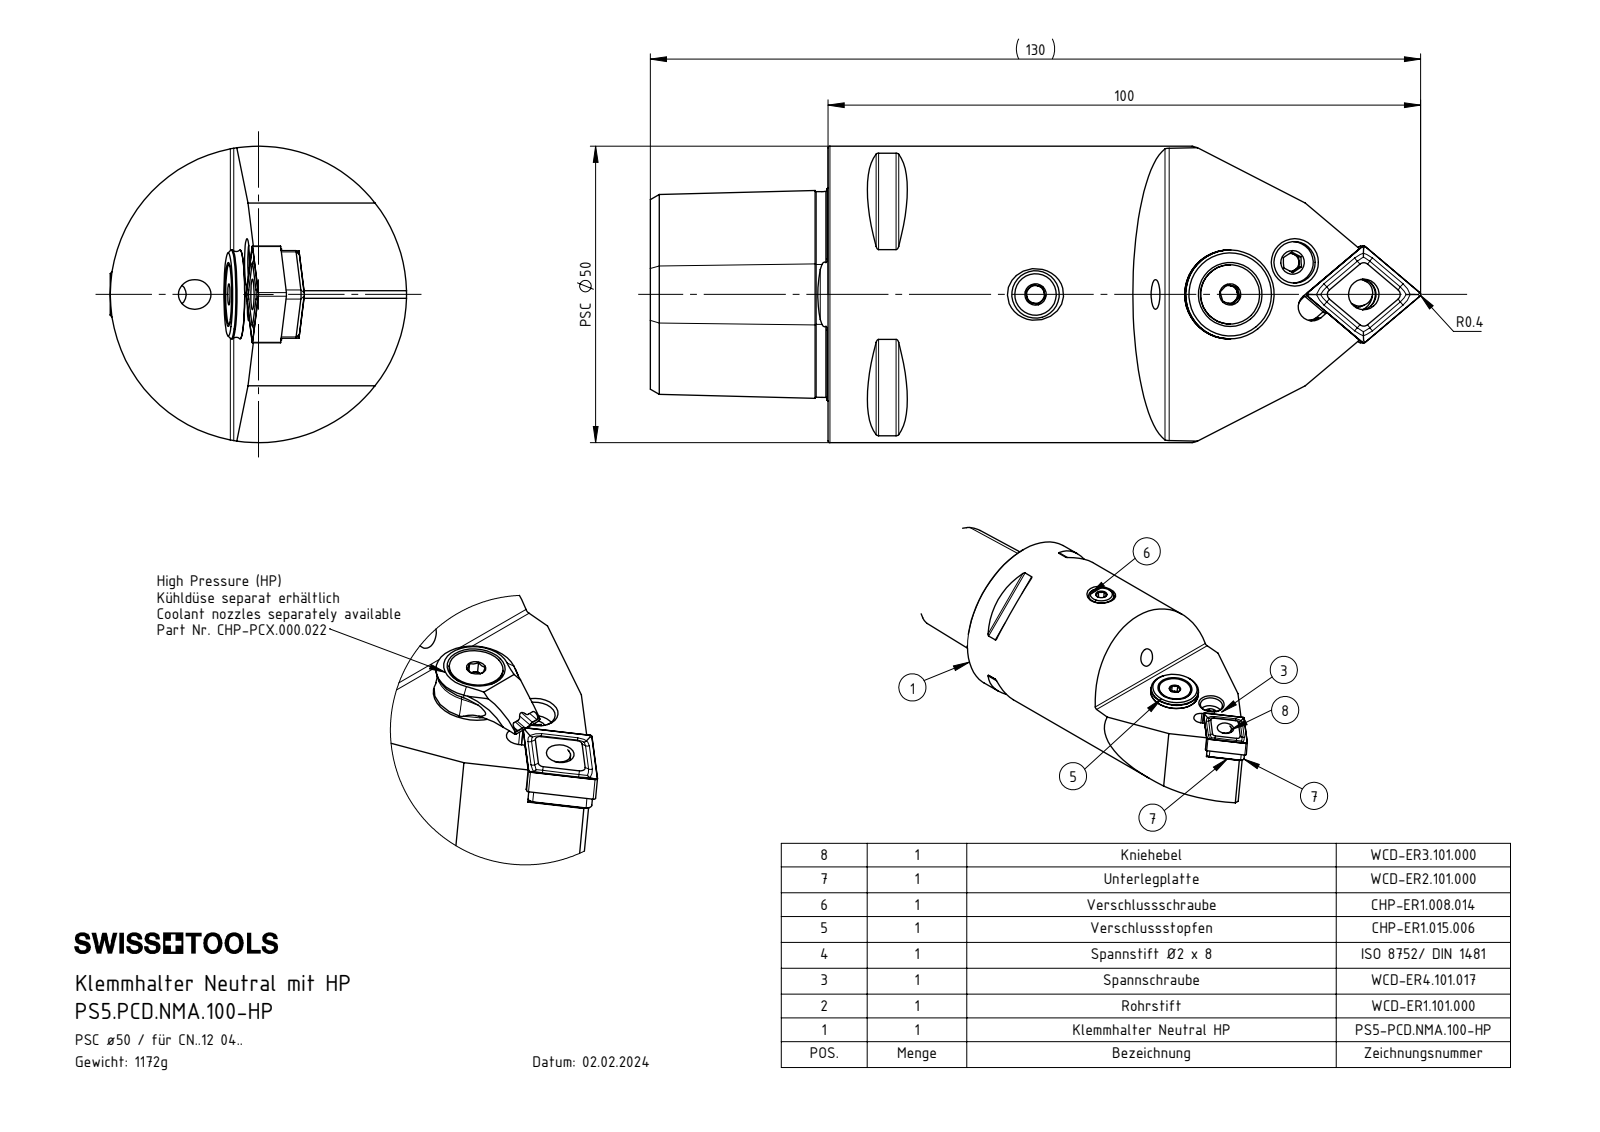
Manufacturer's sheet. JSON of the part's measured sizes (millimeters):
{"part_name": "PS5.PCD.NMA.100-HP; WCD-ER2.101.003_A; ISO 8752 2x8; WCD-ER1.101.000 (+8 more)", "step_written_by": "SolidWorks 2022 (AUTOMOTIVE_DESIGN)", "units": "millimeters", "bodies": {"solids": 12, "faces": 541, "planar": 144, "cylindrical": 146, "other": 251}, "overall_size": [130, 50, 50], "volume_mm3": 148904, "surface_area_mm2": 30141, "round_holes": [[5, 2], [7, 2], [1.2, 1], [2, 1], [3, 1], [3.3, 1], [4, 1], [4.2, 1], [5.16, 1], [5.3, 1], [6.1, 1], [6.55, 1]], "round_bosses_or_shafts": [[8, 2], [50, 1], [14.85, 1], [13.4, 1], [10, 1], [7.9, 1], [6.4, 1], [5.5, 1]], "partial_cylinders_radius": [[1, 11], [0.5, 10], [0.4, 4], [2.5, 3], [6, 3], [1.1, 2], [1.2, 2], [3.2, 2]], "face_to_face_distances": [30, 11.79, 4.46, 19.18, 4.51, 3.13, 3.18, 7.64, 44.4, 0.5], "hole_center_spacings": [4.51, 4.5, 4.52, 8.09, 8.1, 12.42, 12.43, 12.85]}
